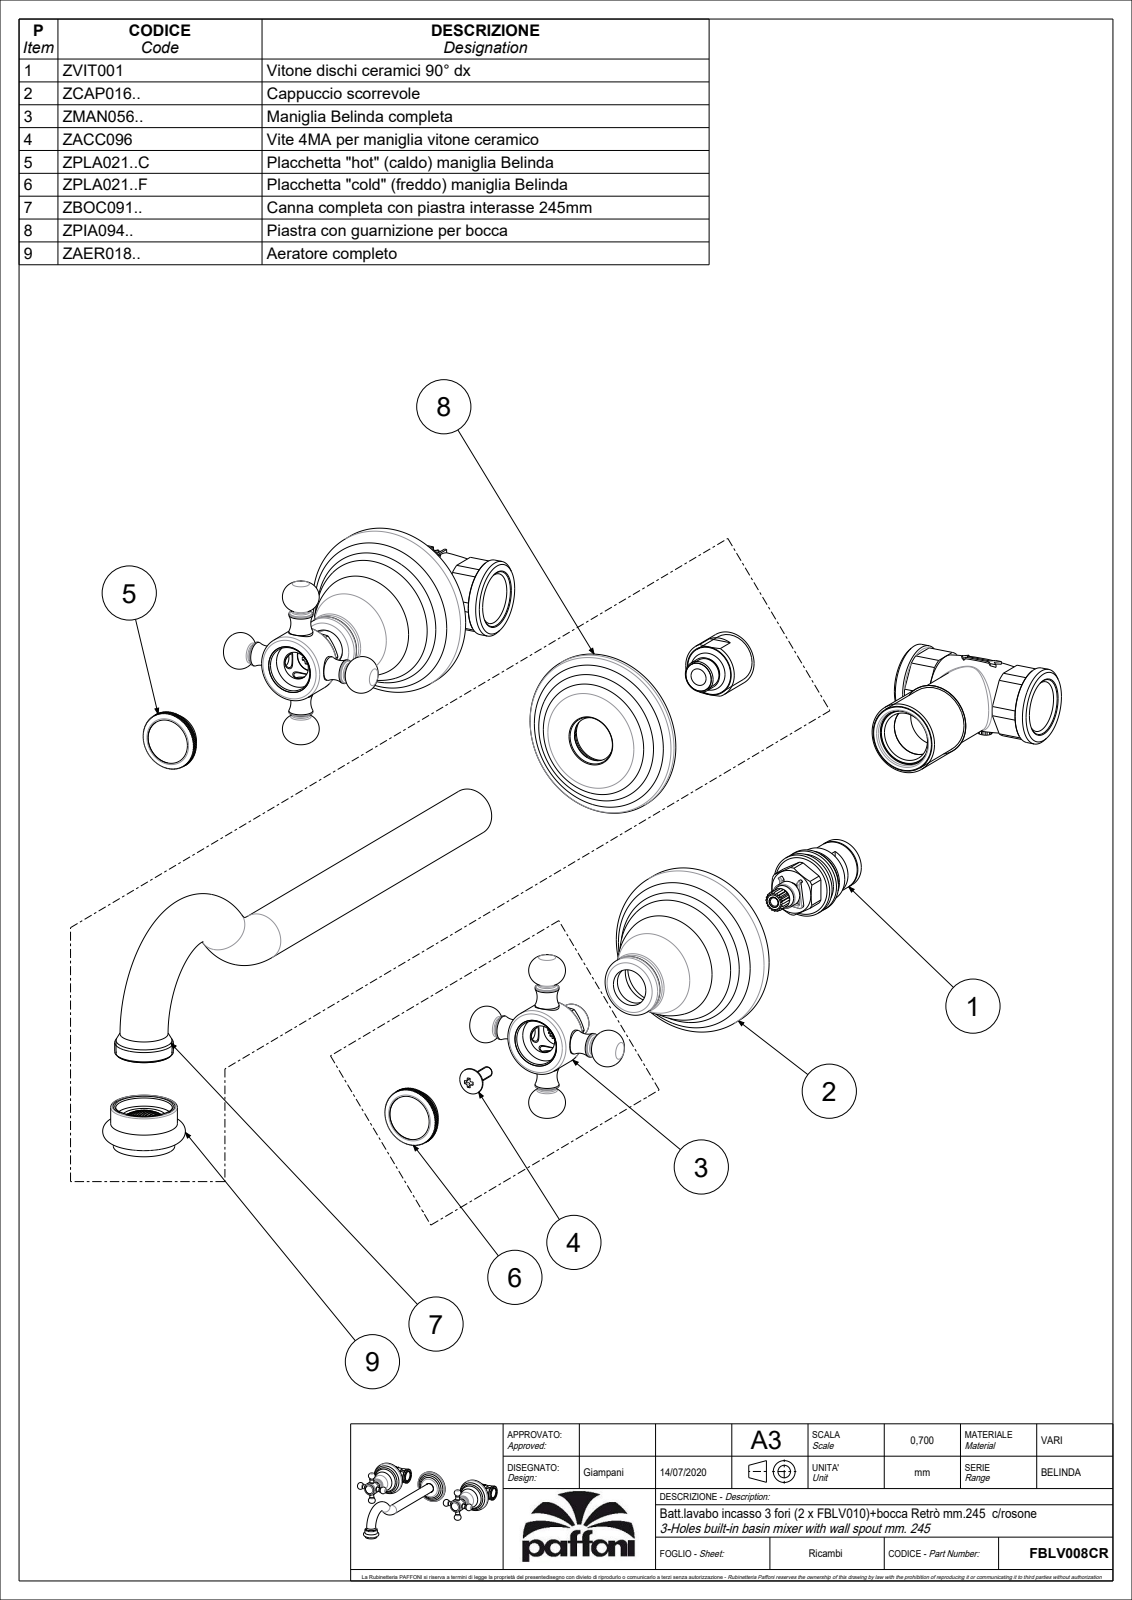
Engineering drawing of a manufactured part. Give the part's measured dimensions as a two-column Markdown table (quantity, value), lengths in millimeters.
| quantity | value |
| --- | --- |
| part name | FBLV008CR |
| STEP written by | CREO PARAMETRIC BY PTC INC, 2020044 (CONFIG_CONTROL_DESIGN) |
| units | millimeters |
| bodies | 3 solids, 917 faces (439 planar, 282 cylindrical, 196 other) |
| overall size | 264.07 × 260.5 × 64.07 |
| volume | 271 103 mm³ |
| surface area | 55 830 mm² |
| round bosses / shafts (diameter × count) | 25 × 3, 9 × 3, 7 × 3, 63 × 2, 22.5 × 2, 14 × 2, 13 × 2, 62 × 1 |
| partial cylindrical surfaces (radius × count) | 11 × 2 |
| main face-to-face distances | 10, 63.5, 53.5, 50, 40, 13.5, 15, 15.2, 173.2, 4 |
